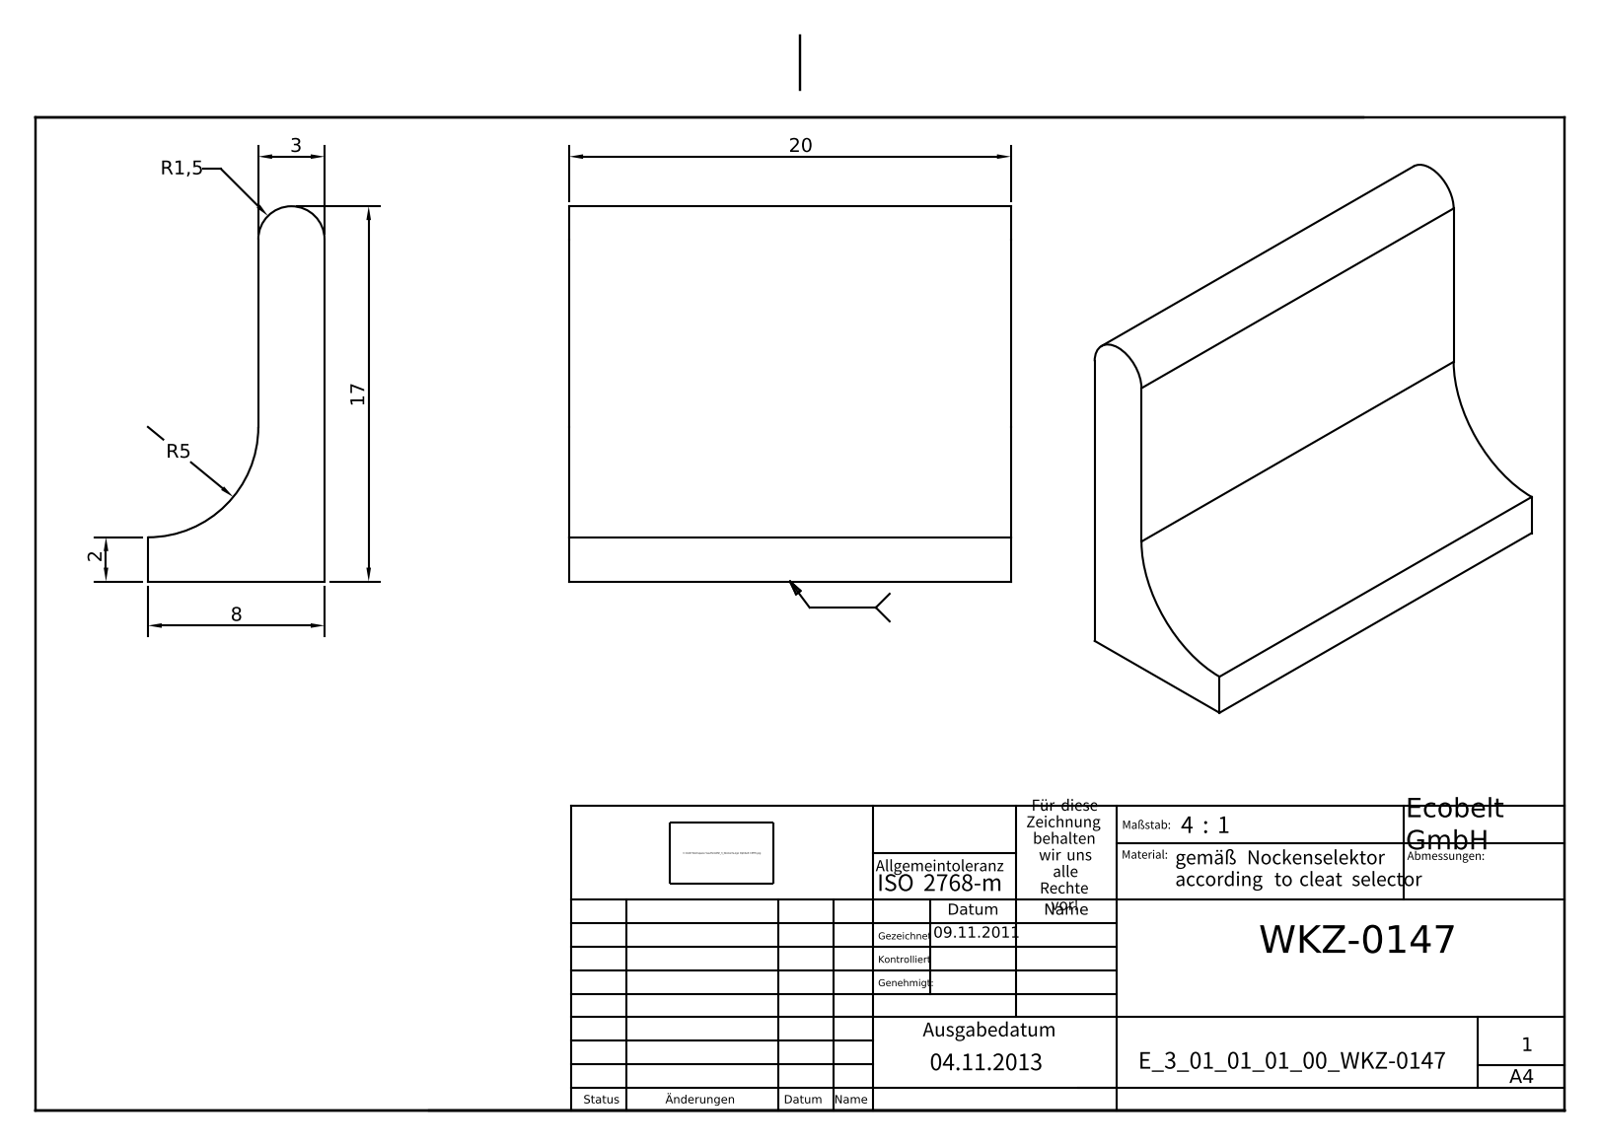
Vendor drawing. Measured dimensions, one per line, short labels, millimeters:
name: E_3_01_01_01_00_WKZ-0147
written by: Autodesk Inventor 2021 (AUTOMOTIVE_DESIGN)
unit: mm
bodies: 1 solid, 8 faces (6 planar, 2 cylindrical, 0 other)
size: 20 × 17 × 8
volume: 1 308 mm³; area: 1 062 mm²
rounds: 1× R1.5, 1× R5
face distances: 3, 20, 5, 8
